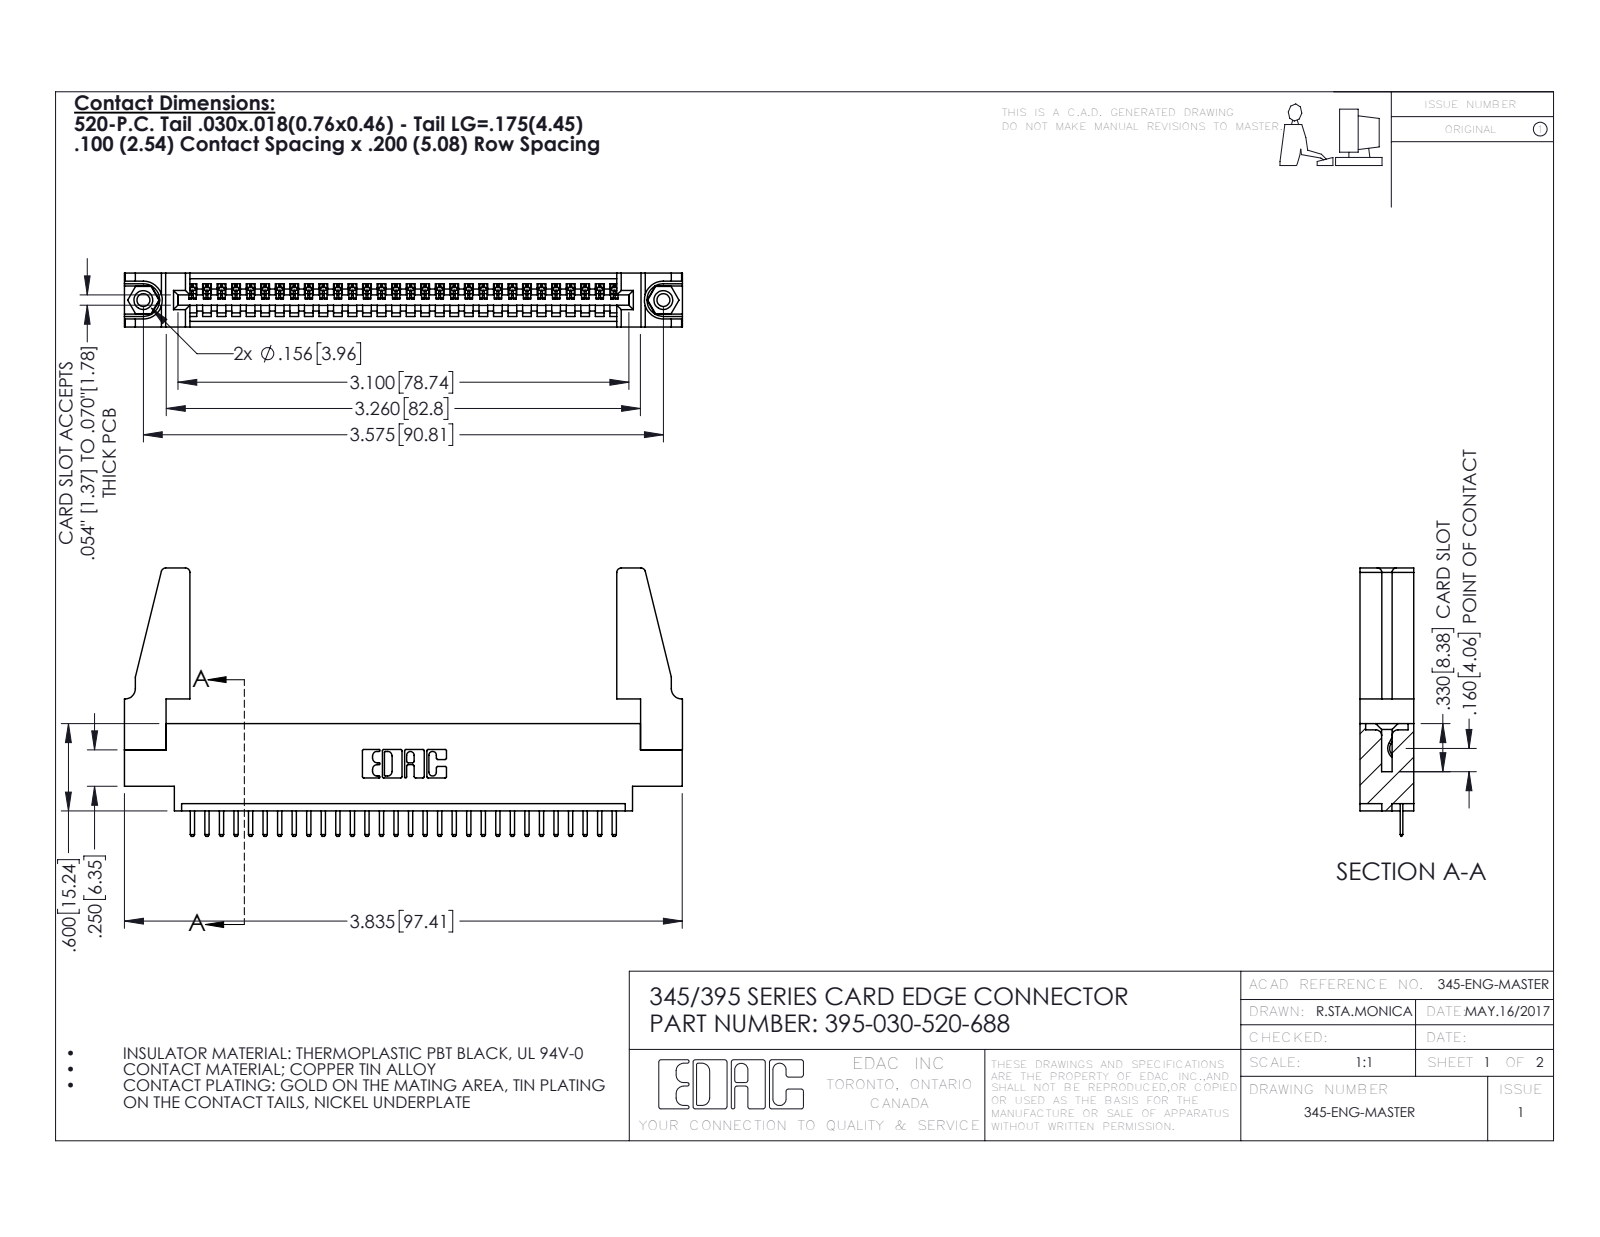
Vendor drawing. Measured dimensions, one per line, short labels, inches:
name: 345-220-078_345-220-088; 345 Part_0.170 Offset - 0.156 Dia-TH; 395-030-520-688; 345-250-001_345-250-001-102 (+1 more)
written by: SolidWorks 2016 (CONFIG_CONTROL_DESIGN)
unit: in
bodies: 35 solids, 2114 faces (1416 planar, 682 cylindrical, 16 other)
size: 3.836 × 1.845 × 0.37
volume: 0.745 in³; area: 22.8 in²
holes: 2× ⌀0.089, 2× ⌀0.125, 2× ⌀0.156, 1× ⌀0.064
bosses: 2× ⌀0.155
rounds: 62× R0.01, 60× R0.006, 22× R0.01, 8× R0.03, 6× R0.007, 6× R0.031, 3× R0.026, 2× R0.031
face distances: 0.37, 0.072, 0.298, 0.2, 0.098, 0.272, 0.025, 0.225, 0.072, 0.175
hole spacings: 0.27, 3.34, 3.575
